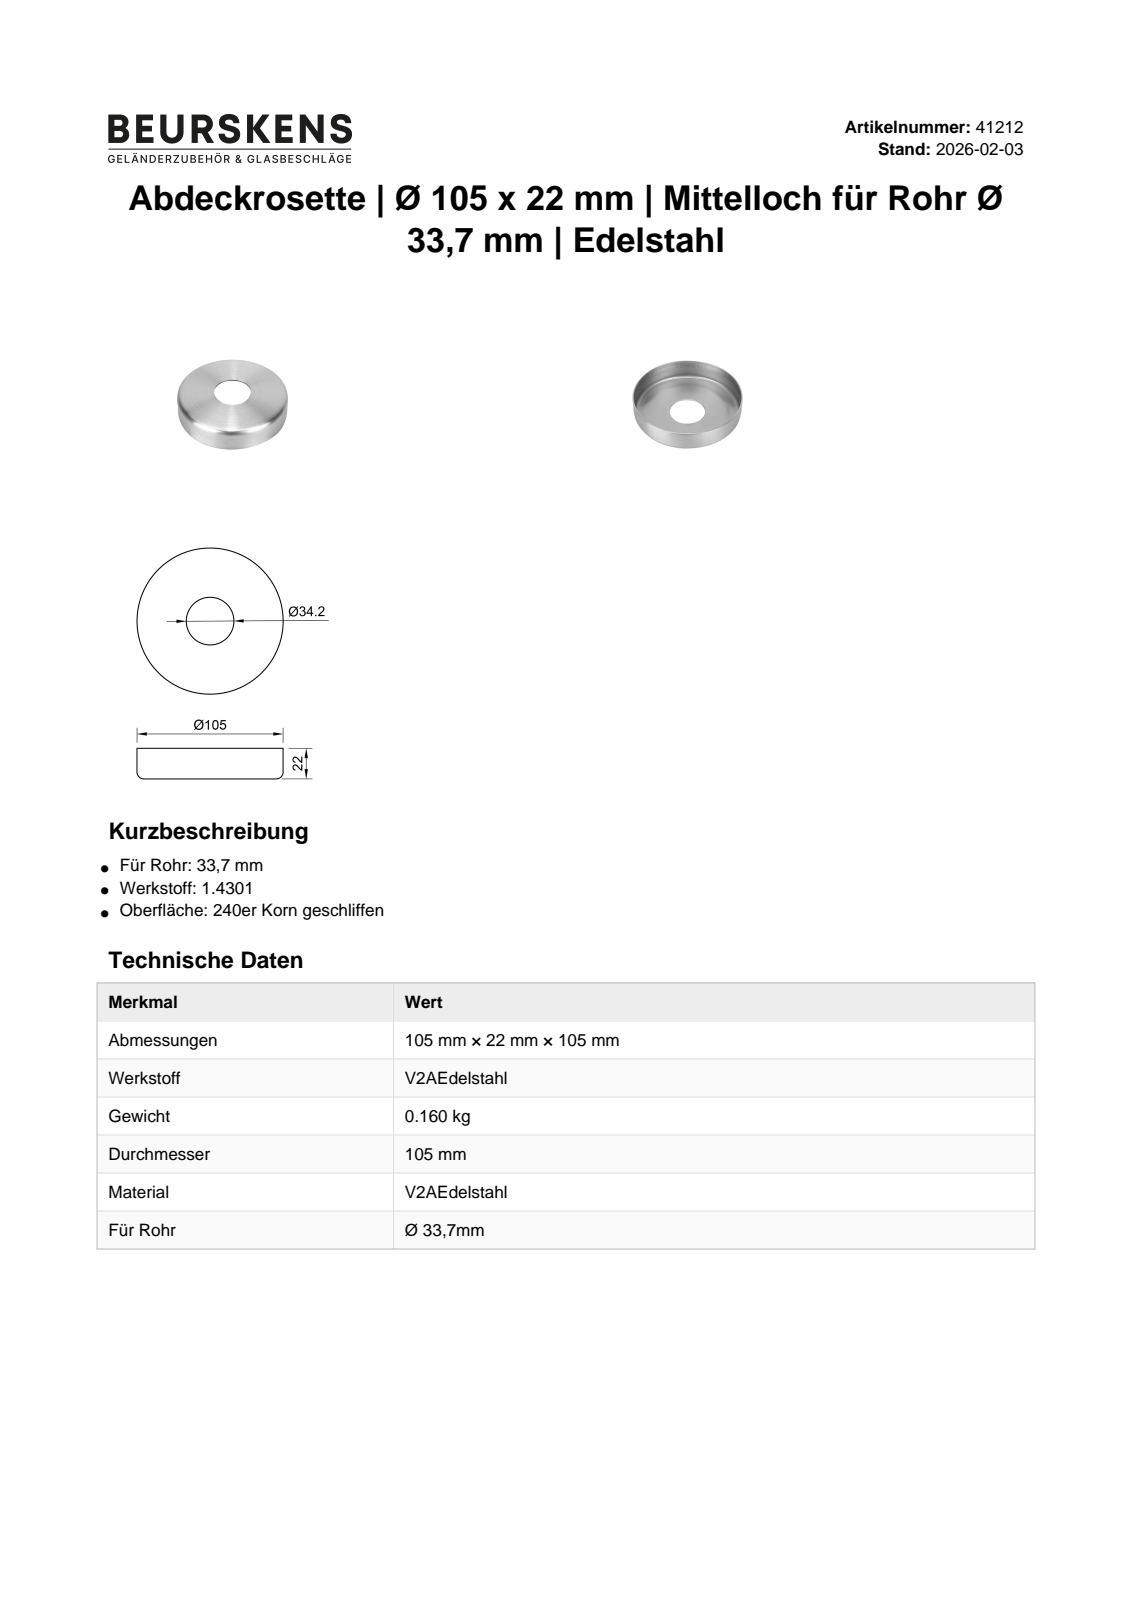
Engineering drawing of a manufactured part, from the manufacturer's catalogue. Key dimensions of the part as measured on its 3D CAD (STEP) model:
Part name (STEP PRODUCT): 41212
STEP written by: Autodesk Inventor 2022 (AUTOMOTIVE_DESIGN)
Units: millimetres
Bodies: 1 solid, 7 faces (3 planar, 3 cylindrical, 1 other)
Overall size (bounding box): 105 × 105 × 22
Volume: 19 877 mm³ · Surface area: 28 749 mm²
Round holes (diameter × count): ⌀34.2 ×1, ⌀102 ×1
Round bosses / shafts (diameter × count): ⌀105 ×1
Main face-to-face distances: 1.5, 20.5, 22
